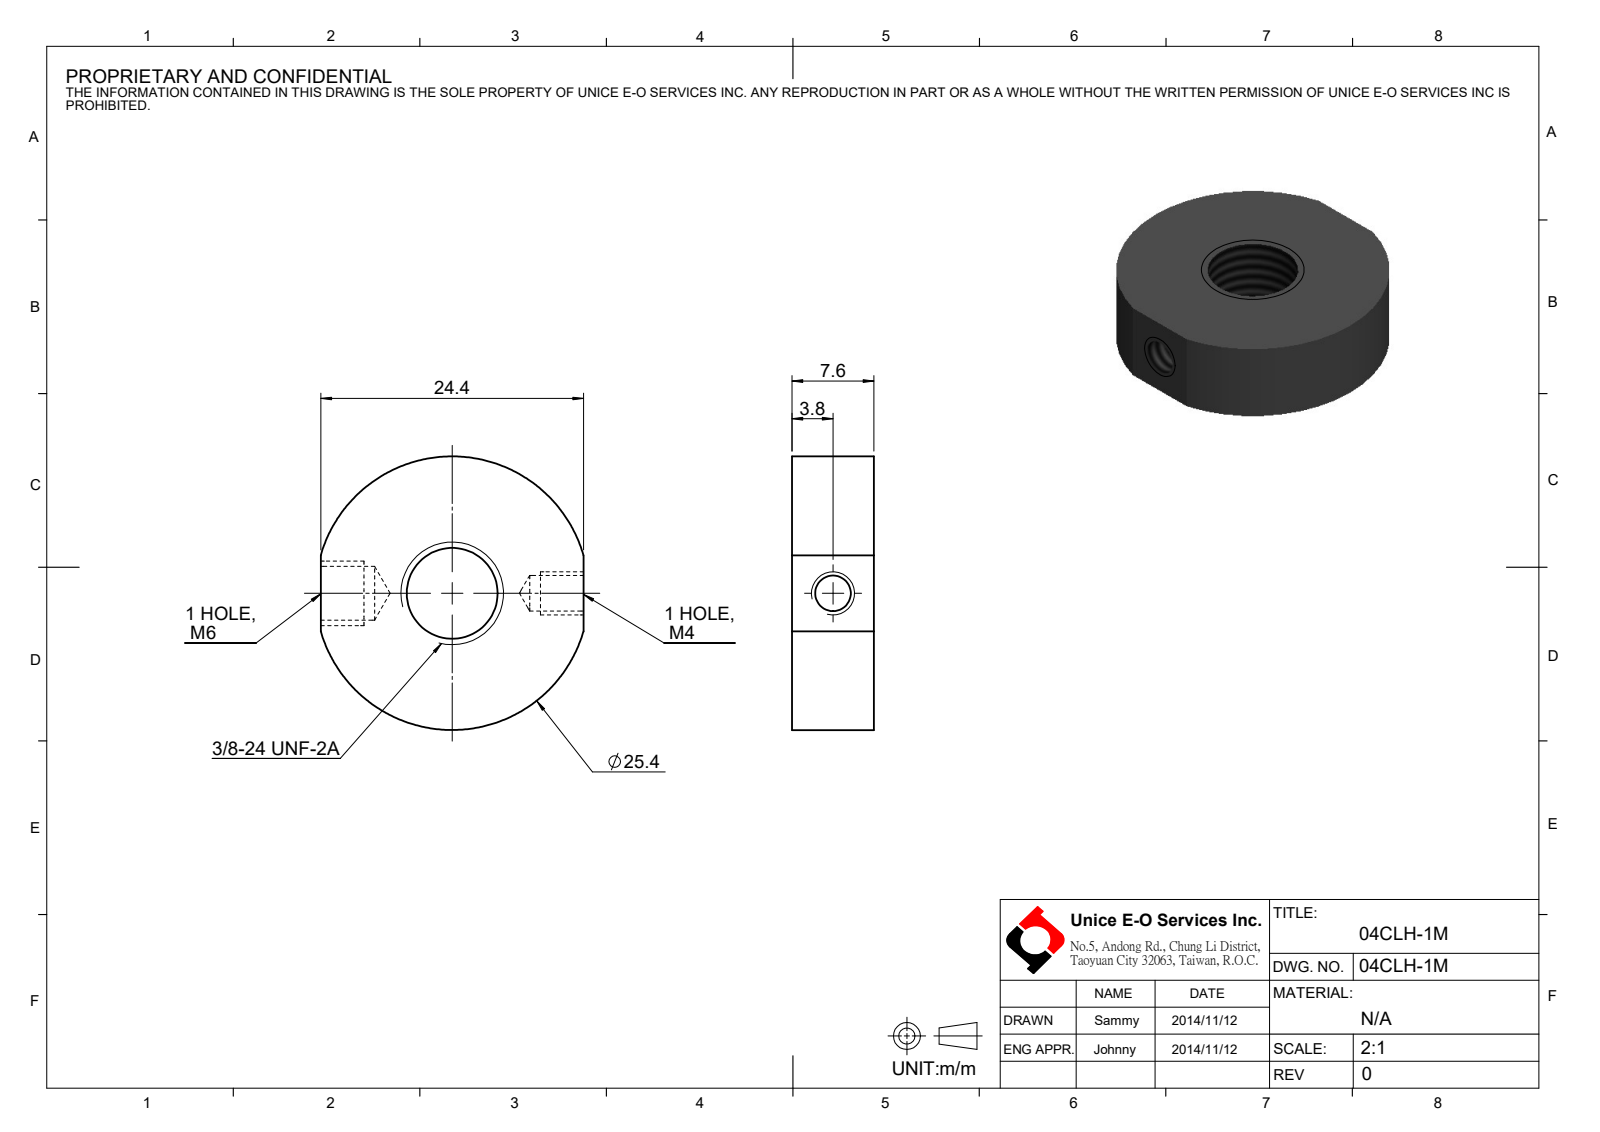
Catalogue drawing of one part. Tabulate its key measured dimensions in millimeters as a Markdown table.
| quantity | value |
| --- | --- |
| part name | 04CLH-1M |
| STEP written by | SolidWorks 2016 (CONFIG_CONTROL_DESIGN) |
| units | millimeters |
| bodies | 1 solid, 16 faces (4 planar, 8 cylindrical, 4 other) |
| overall size | 25.4 × 24.4 × 7.6 |
| volume | 3 238 mm³ |
| surface area | 1 833 mm² |
| round holes (diameter × count) | 3.3 × 1, 5 × 1, 8.43 × 1 |
| round bosses / shafts (diameter × count) | 25.4 × 1 |
| main face-to-face distances | 7.6, 24.4 |
